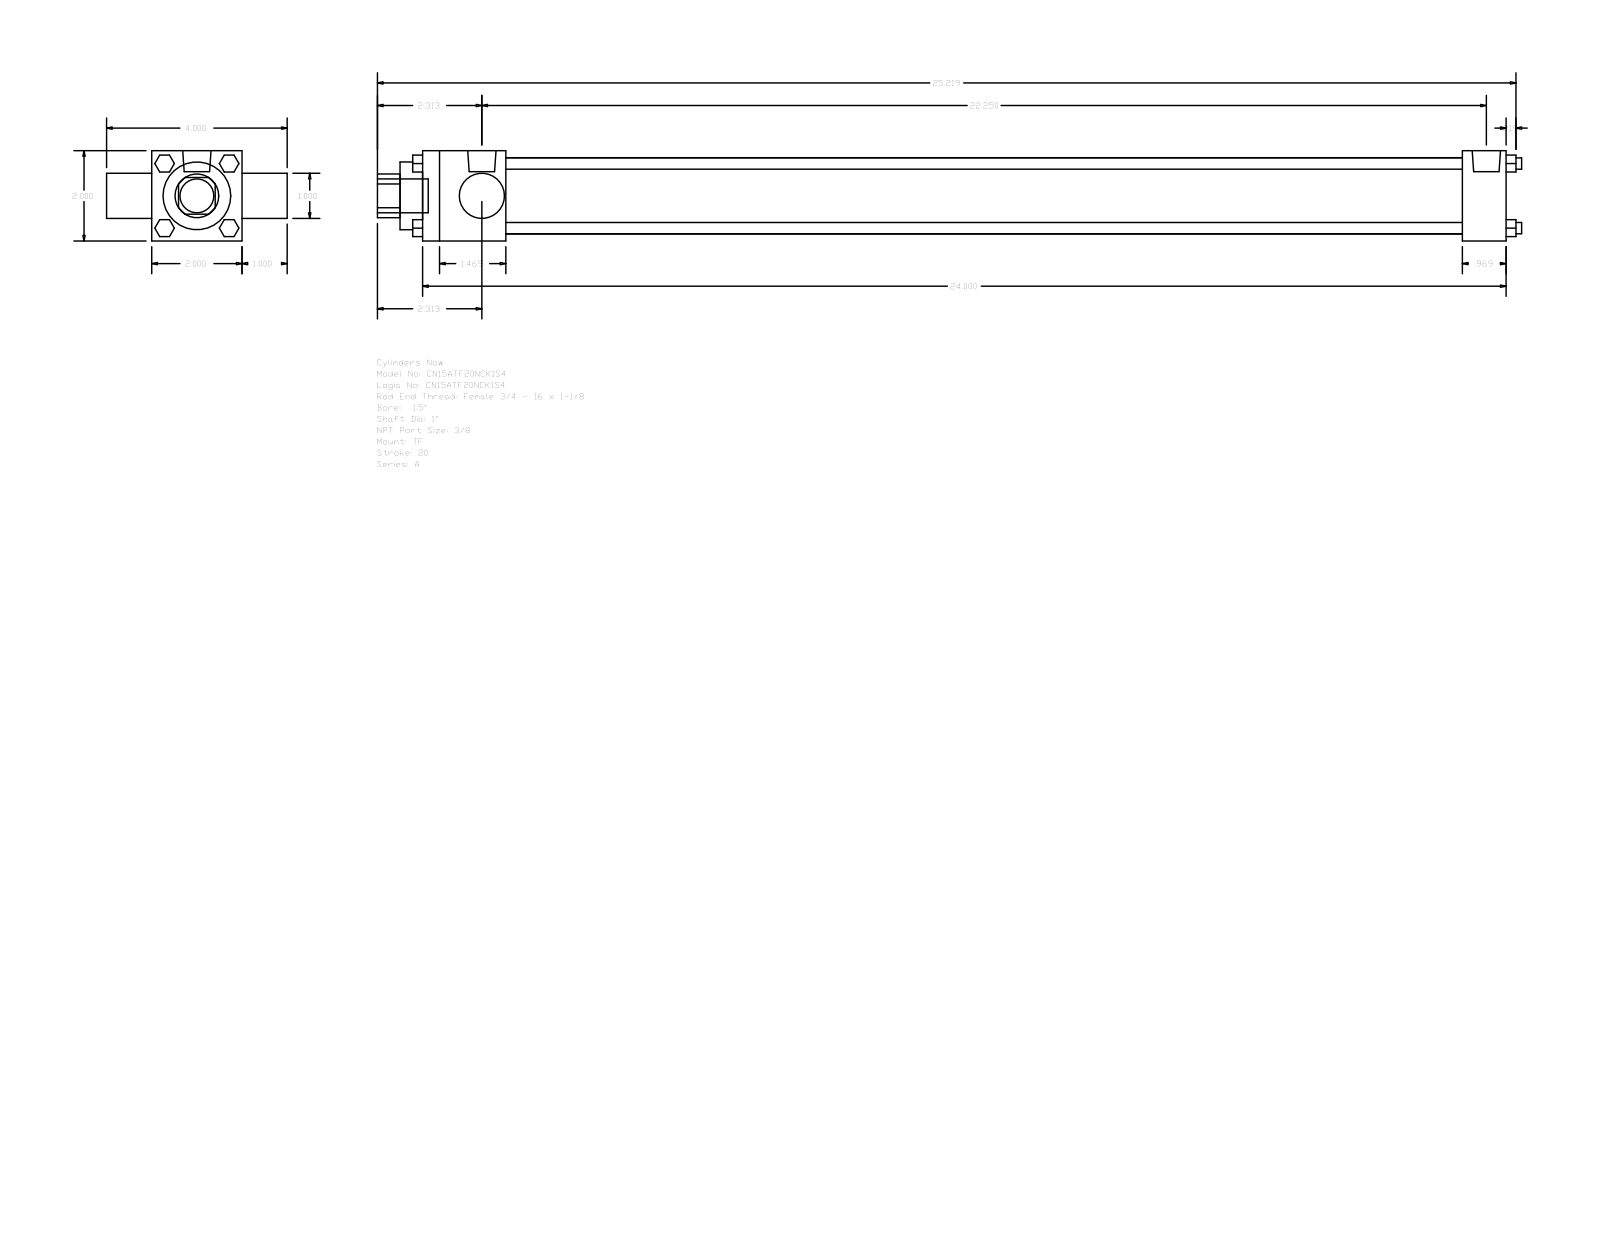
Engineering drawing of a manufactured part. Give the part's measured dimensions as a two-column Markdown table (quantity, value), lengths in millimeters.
| quantity | value |
| --- | --- |
| part name | A_TF__0150_1 |
| STEP written by | GSSL Pune (CONFIG_CONTROL_DESIGN) |
| units | millimeters |
| bodies | 0 solids, 120 faces (92 planar, 28 cylindrical, 0 other) |
| overall size | 643.73 × 101.6 × 50.8 |
| round holes (diameter × count) | 25.4 × 2, 38.1 × 1, 42.93 × 1 |
| round bosses / shafts (diameter × count) | 6.35 × 4, 5.56 × 3, 15.93 × 2, 19.05 × 1 |
| partial cylindrical surfaces (radius × count) | 12.29 × 1 |
| main face-to-face distances | 50.8, 25.4, 609.6, 76.2, 46.83, 584.99, 538.16, 562.77, 24.61, 12.7 |
